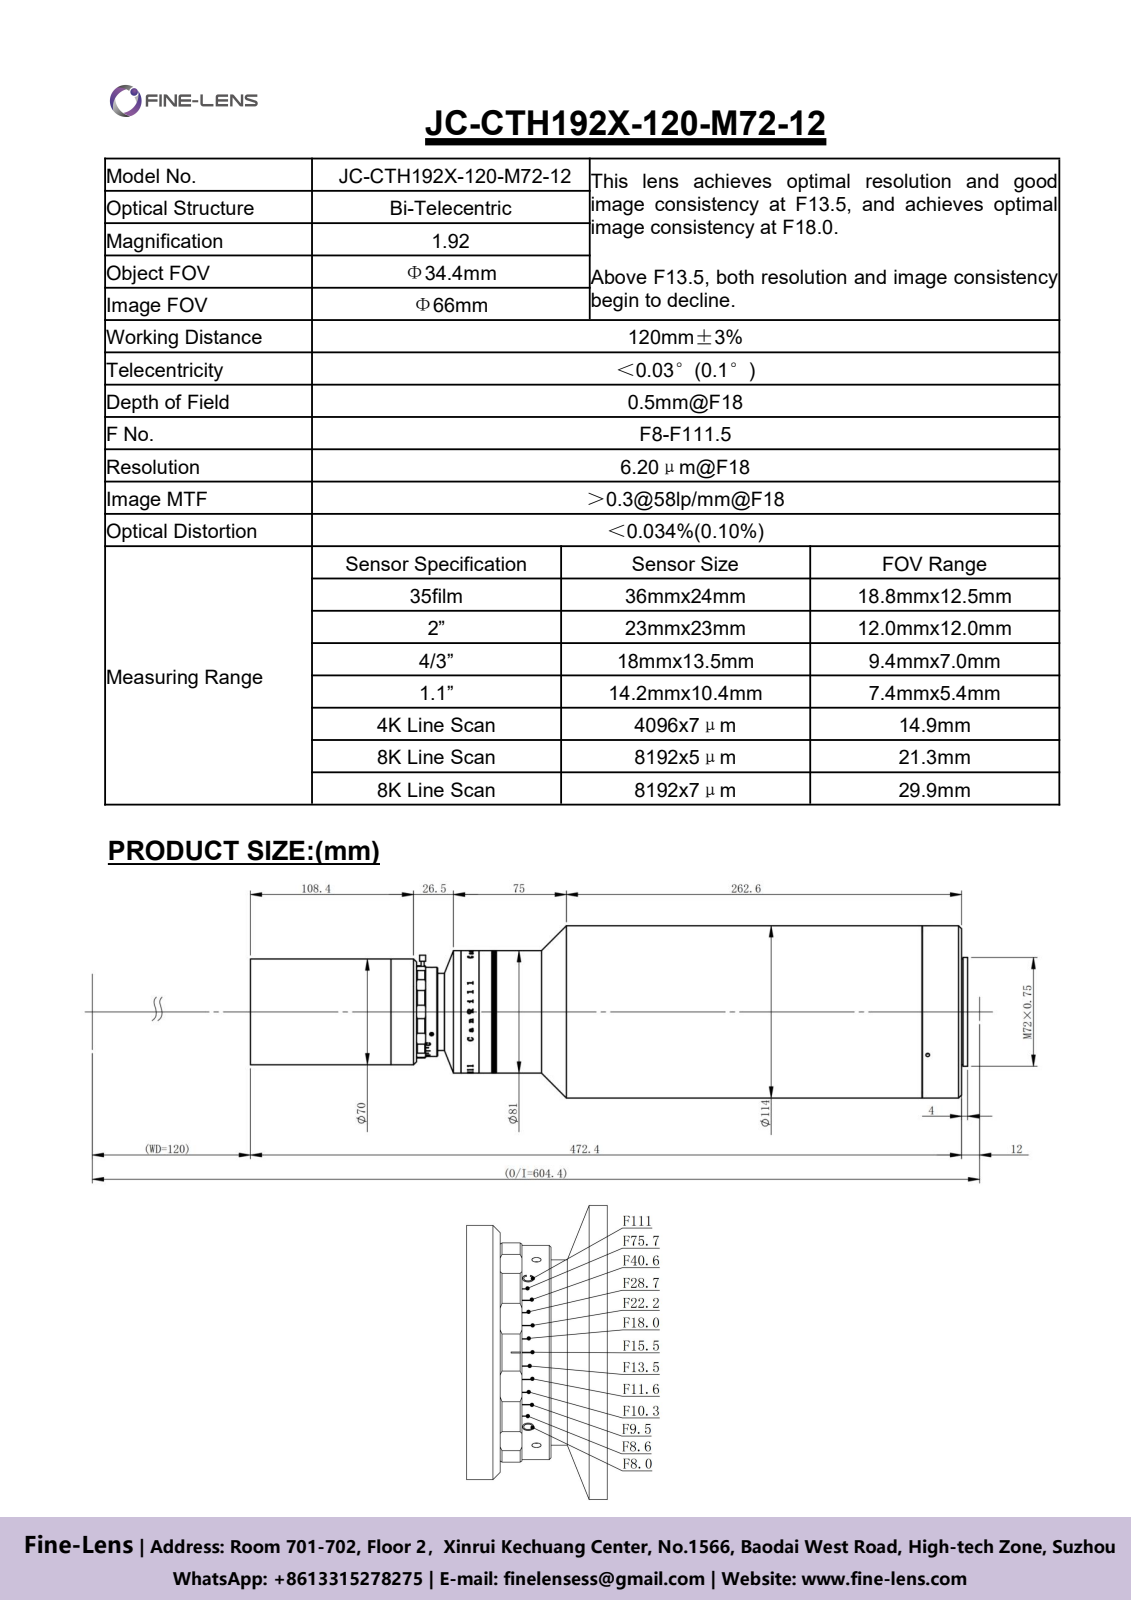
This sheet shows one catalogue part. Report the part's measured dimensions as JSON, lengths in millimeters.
{"part_name": "XF-PTL04582-M72-12-VI", "step_written_by": "SolidWorks 2014 (CONFIG_CONTROL_DESIGN)", "units": "millimeters", "bodies": {"solids": 0, "faces": 225, "planar": 37, "cylindrical": 153, "other": 35}, "overall_size": [476.42, 114, 114], "round_holes": [[2.5, 6], [65, 1], [68, 1], [101, 1]], "round_bosses_or_shafts": [[114, 1], [81, 1], [72, 1], [70, 1], [63, 1], [61, 1], [59, 1], [51, 1]], "partial_cylinders_radius": [[15, 10], [29.4, 1], [40.49, 1]], "face_to_face_distances": [309.05, 335.75, 6, 53, 362.05, 26, 336.05, 283.05, 282.75, 26.3], "hole_center_spacings": [329.55]}
